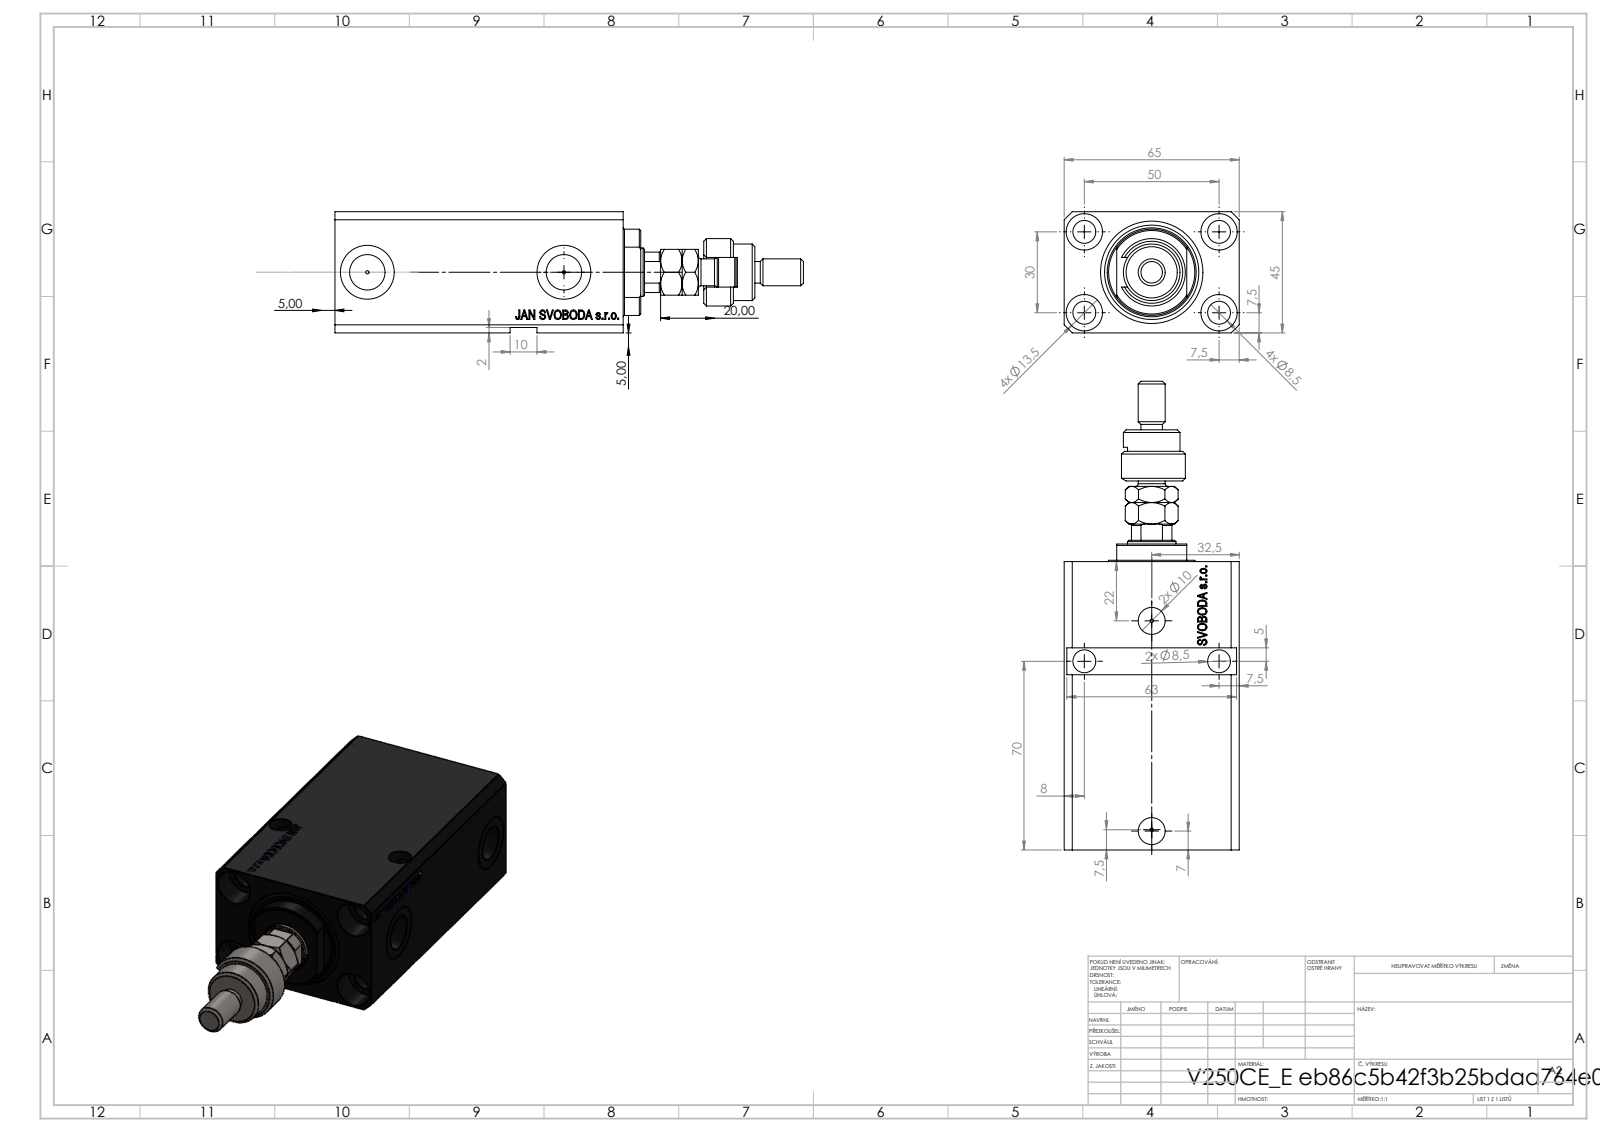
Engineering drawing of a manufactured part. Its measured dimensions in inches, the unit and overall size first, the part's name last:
Units: inches
Overall size (bounding box): 6.85 × 2.559 × 1.772
Round holes (diameter × count): ⌀0.335 ×9, ⌀0.049 ×4, ⌀0.531 ×4, ⌀0.394 ×2, ⌀0.518 ×2, ⌀0.787 ×2, ⌀0.709 ×1, ⌀1.496 ×1
Round bosses / shafts (diameter × count): ⌀0.984 ×1, ⌀0.827 ×1, ⌀0.63 ×1, ⌀0.394 ×1, ⌀0.315 ×1
Partial cylindrical surfaces — rounded edges, fillets, slot ends (radius × count): R0.217 ×1, R0.335 ×1, R0.344 ×1, R0.63 ×1
Main face-to-face distances: 1.772, 2.559, 0.551, 3.661, 4.213, 0.272, 3.39, 3.941, 1.102, 1.693
Hole centre spacings: 1.148, 1.969, 1.181, 1.323, 1.337, 1.575, 2.296, 2.379
Volume: 16.46 in³ · Surface area: 113.9 in²
Bodies: 5 solids, 1018 faces (467 planar, 129 cylindrical, 422 other)
Part name (STEP PRODUCT): V250CE_VC_E; MFA; V250CE_E_Body; V250CE_C_VCP (+1 more)
STEP written by: SolidWorks 2019 (CONFIG_CONTROL_DESIGN)
